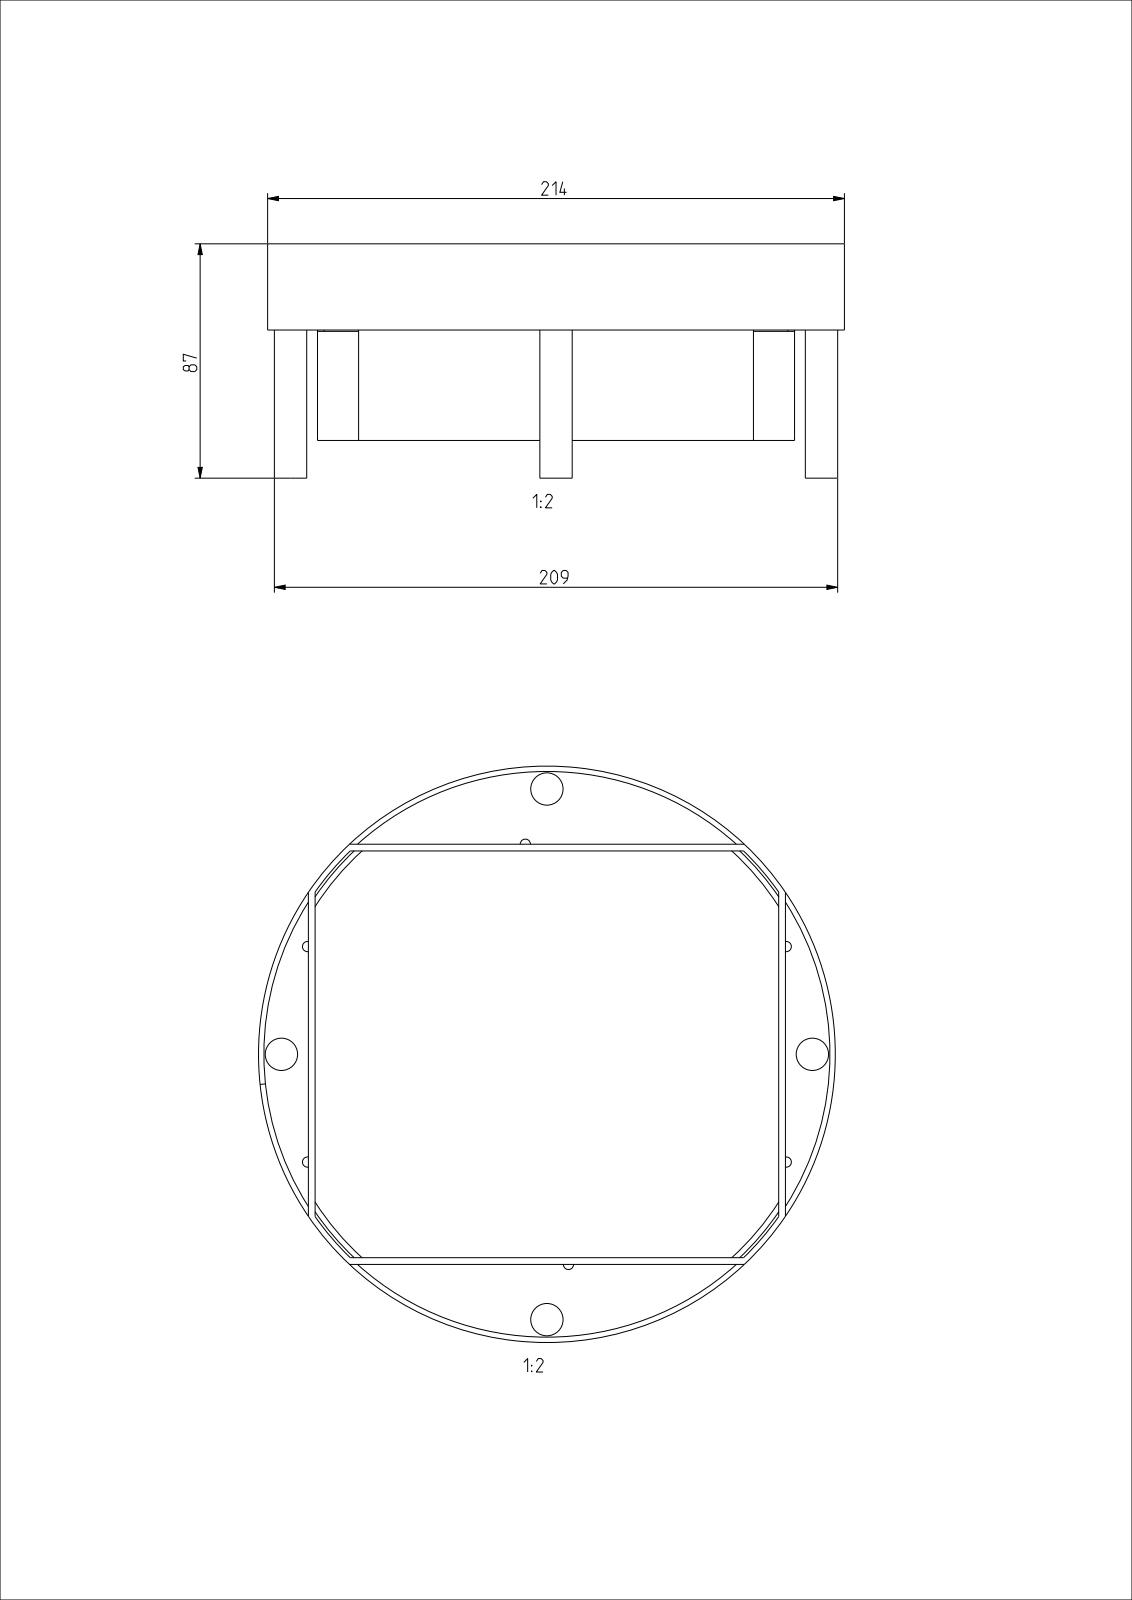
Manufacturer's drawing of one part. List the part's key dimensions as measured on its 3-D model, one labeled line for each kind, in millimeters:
Part name (STEP PRODUCT): T-00702; T-00703; T-00704; T-00709 (+8 more)
STEP written by: CREO PARAMETRIC BY PTC INC, 2022024 (AUTOMOTIVE_DESIGN)
Units: millimetres
Bodies: 8 solids, 132 faces (72 planar, 60 cylindrical, 0 other)
Overall size (bounding box): 305 × 305 × 87
Volume: 377 812 mm³ · Surface area: 425 512 mm²
Round holes (diameter × count): ⌀3.8 ×6, ⌀10.1 ×4
Round bosses / shafts (diameter × count): ⌀12 ×4, ⌀9.85 ×4, ⌀305 ×1, ⌀301 ×1, ⌀299 ×1, ⌀295 ×1
Partial cylindrical surfaces — rounded edges, fillets, slot ends (radius × count): R0.5 ×8, R150 ×1
Main face-to-face distances: 2, 2.5, 5, 7, 228.5, 3, 229.5, 226, 231, 227
Hole centre spacings: 59.51, 143.6, 197.99, 225.52, 260.65, 25.3, 108, 123.66
